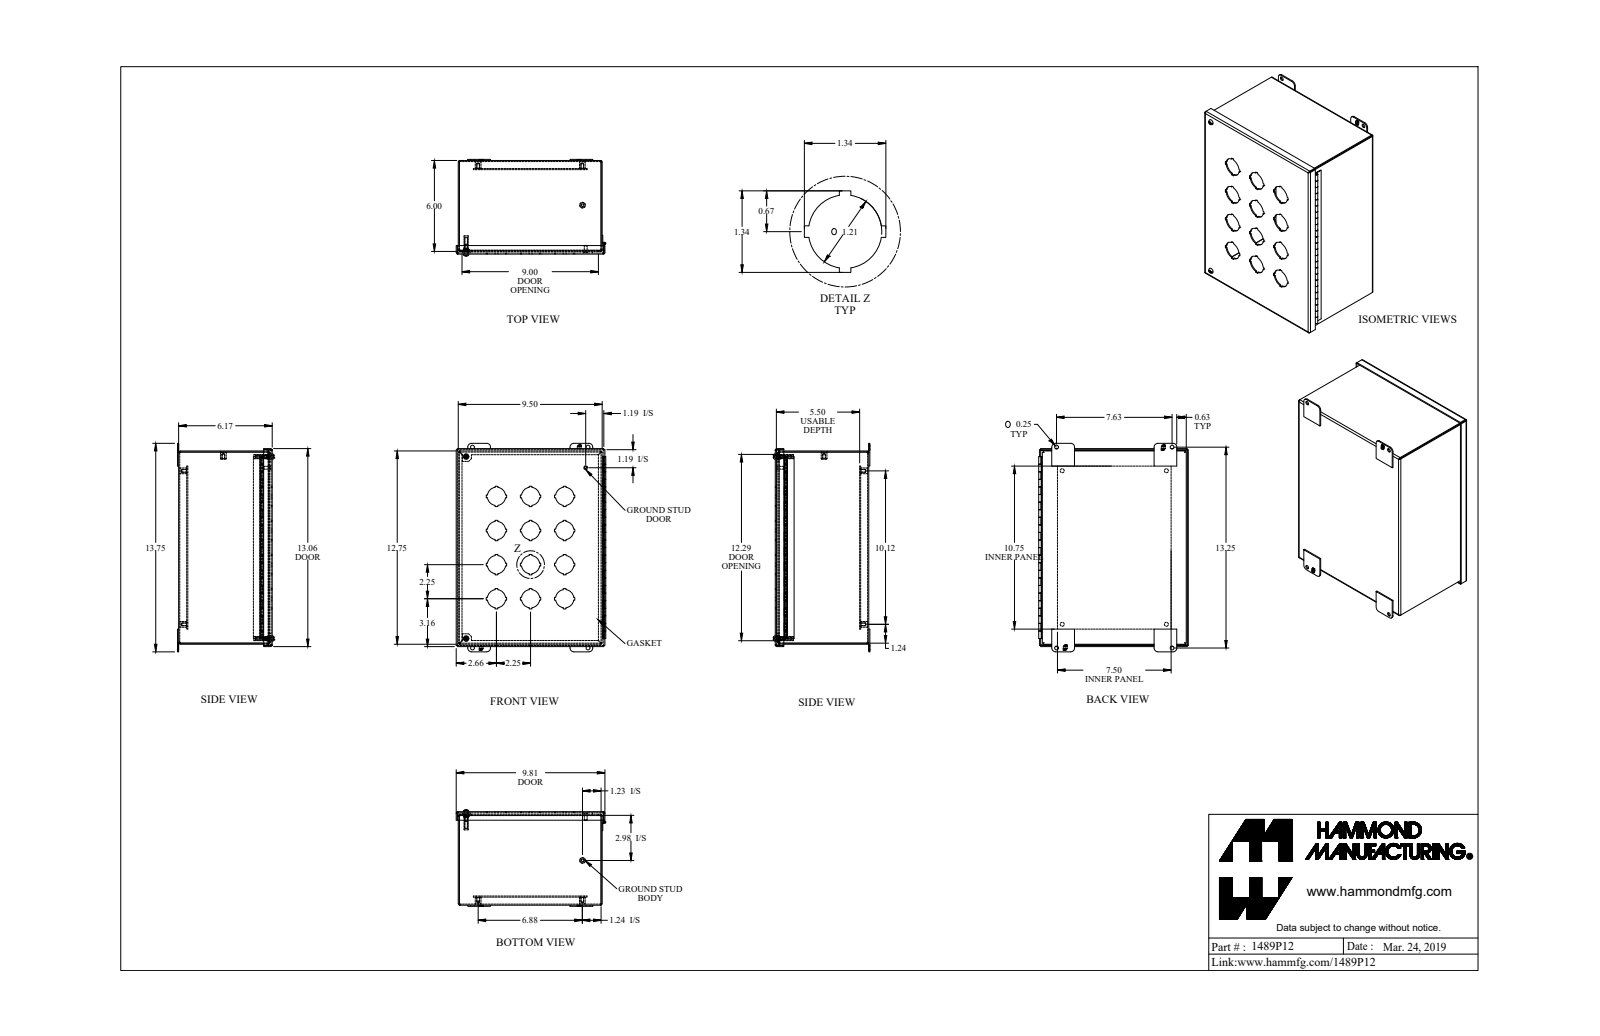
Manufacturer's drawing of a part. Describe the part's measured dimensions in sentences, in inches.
The part is named "1489P12_Default". Its 3-D file was written by "SolidWorks 2019 (CONFIG_CONTROL_DESIGN)". It is 21 solids with 921 faces: 633 planar, 230 cylindrical and 58 other. Overall it measures 13.75 by 9.873 by 6.371 inches. Its volume is 50.91 cubic inches and its surface area 1 363 square inches. Round holes: 12 of diameter 1.21, 6 of diameter 0.25, 5 of diameter 0.156, 4 of diameter 0.265, 2 of diameter 0.159, 2 of diameter 0.406. Round bosses or shafts: 5 of diameter 0.375, 2 of diameter 0.39, 2 of diameter 0.275, 2 of diameter 0.19, 2 of diameter 0.148, 1 of diameter 0.25, 1 of diameter 0.188, 1 of diameter 0.174. Partial cylindrical surfaces (rounded edges, fillets, slot ends): 12 of radius 0.036, 12 of radius 0.108, 8 of radius 0.25, 2 of radius 0.16, 2 of radius 0.171. The main face-to-face distances are 0.072, 6.1, 5.568, 0.532, 9.428, 6.172, 6.028, 12.678, 0.604, 5.64. The hole center spacings are 2.25, 5.031, 3.182, 4.5, 6.875, 7.417, 12, 1.607.
